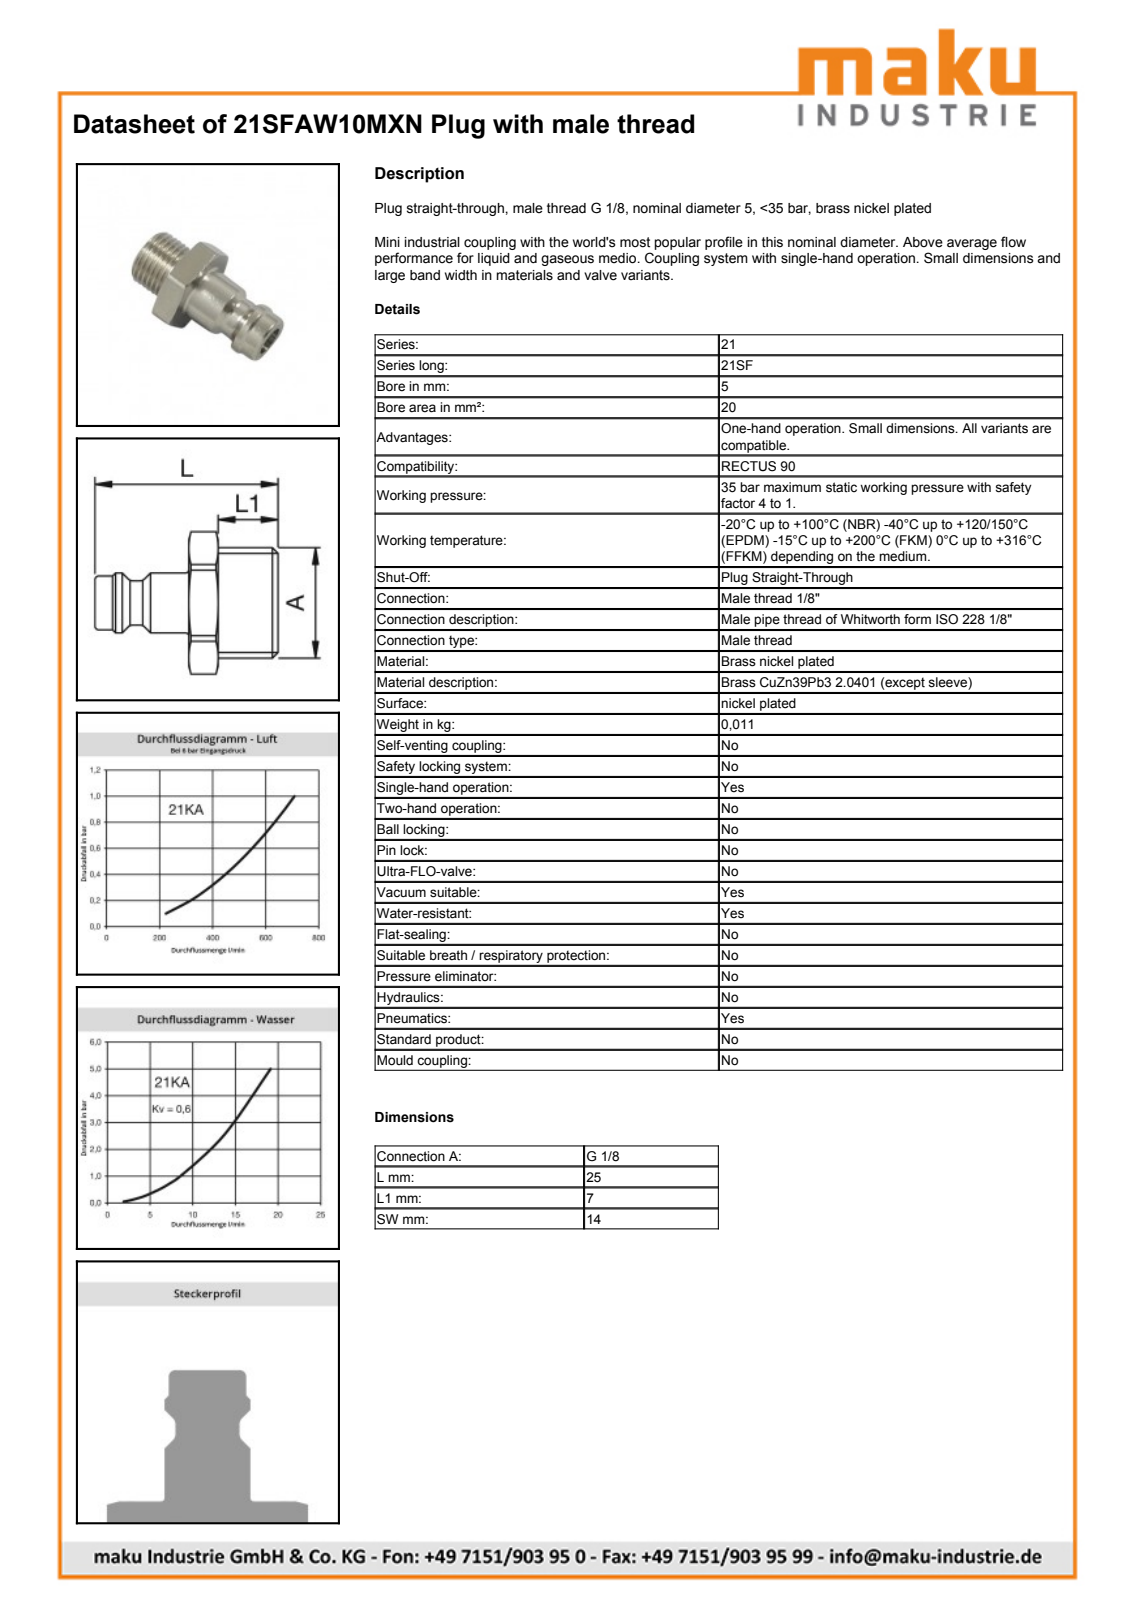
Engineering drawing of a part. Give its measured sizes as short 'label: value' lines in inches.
name: D104294
written by: Autodesk Inventor 2011 (AUTOMOTIVE_DESIGN)
unit: in
bodies: 1 solid, 43 faces (10 planar, 12 cylindrical, 21 other)
size: 0.984 × 0.622 × 0.551
volume: 0.087 in³; area: 2.221 in²
holes: 1× ⌀0.195
bosses: 1× ⌀0.383, 1× ⌀0.354, 1× ⌀0.319, 1× ⌀0.262
rounds: 1× R0.311
face distances: 0.551, 0.154, 0.555, 0.709, 0.984, 0.429, 0.276
